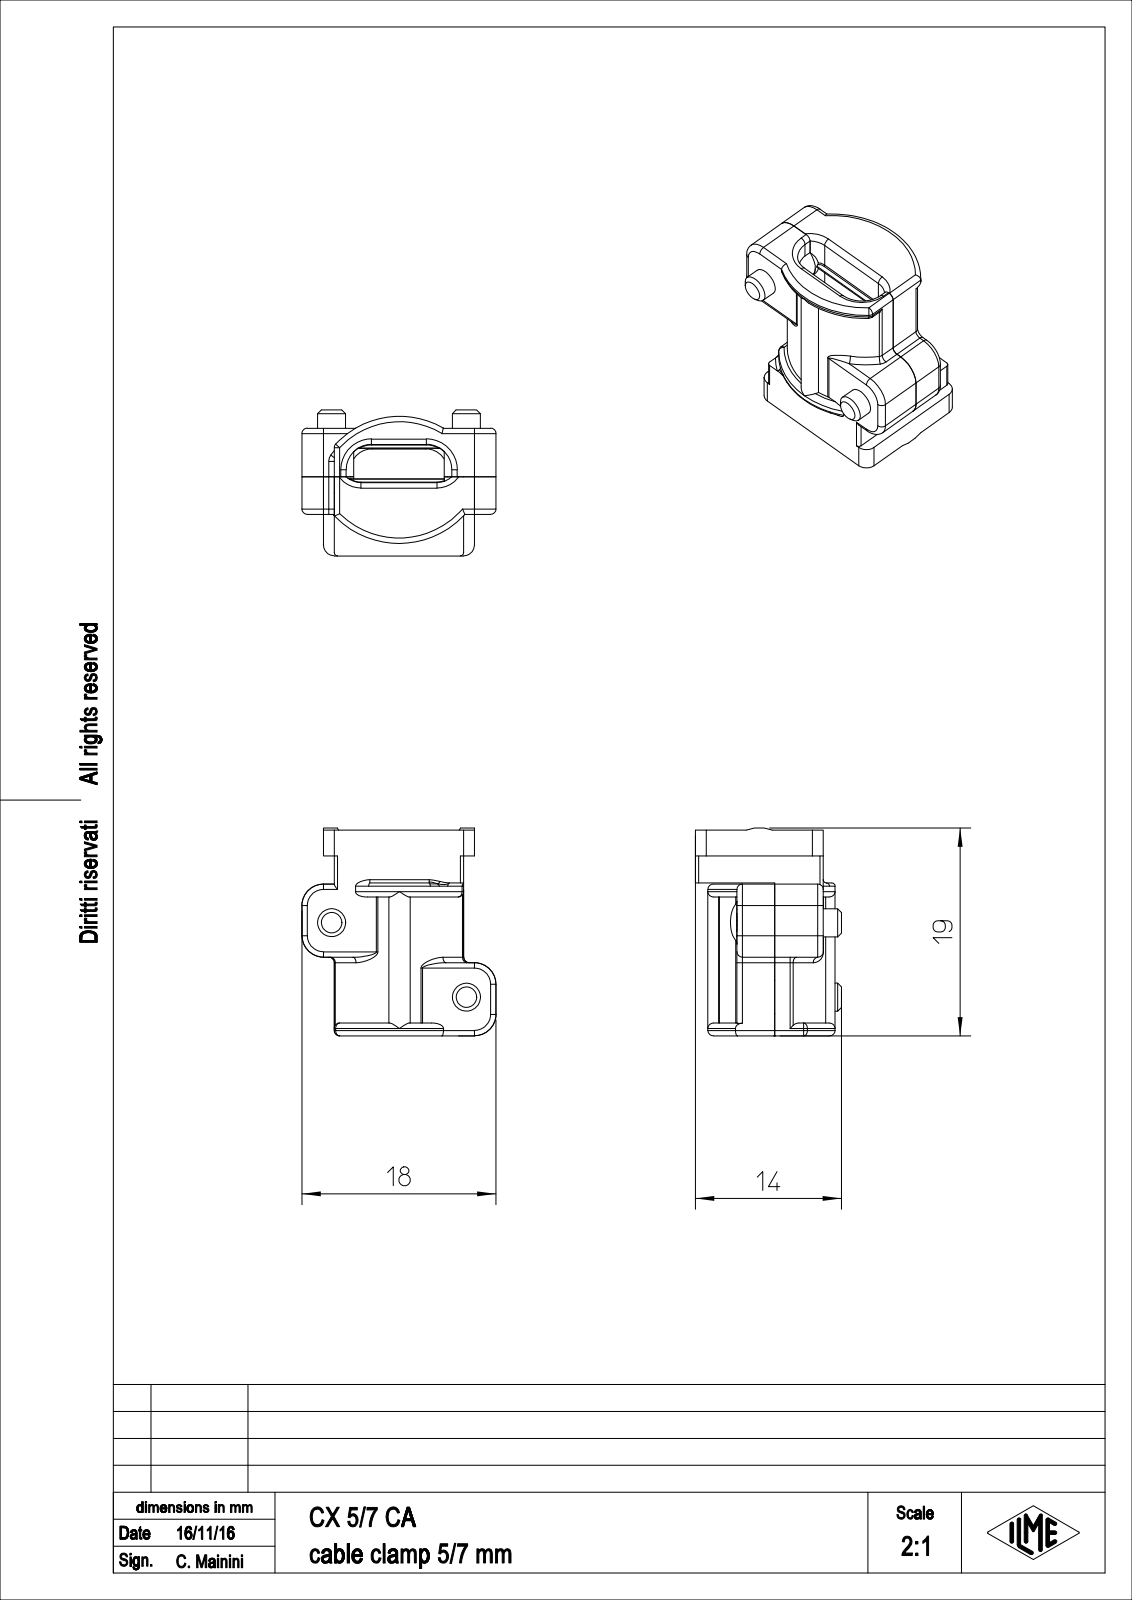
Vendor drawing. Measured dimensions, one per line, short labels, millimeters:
name: CX_5-7_CA
written by: PTC Creo Elements/Direct Modeling 19.0E 27-Jun-2016 (C) Parametric Technology GmbH (AUTOMOTIVE_DESIGN)
unit: mm
bodies: 1 solid, 422 faces (123 planar, 150 cylindrical, 149 other)
size: 19.3 × 18 × 13.55
volume: 1 813 mm³; area: 1 928 mm²
holes: 2× ⌀2.65
bosses: 2× ⌀2.6, 2× ⌀2.2
rounds: 44× R0.2, 37× R0.5, 10× R2, 6× R0.1, 6× R1, 5× R0.3, 4× R2.05, 2× R2.25
face distances: 1.5, 5.05, 19.1, 6.8, 12, 8, 11.85, 2.5, 5, 13
hole spacings: 14.33
